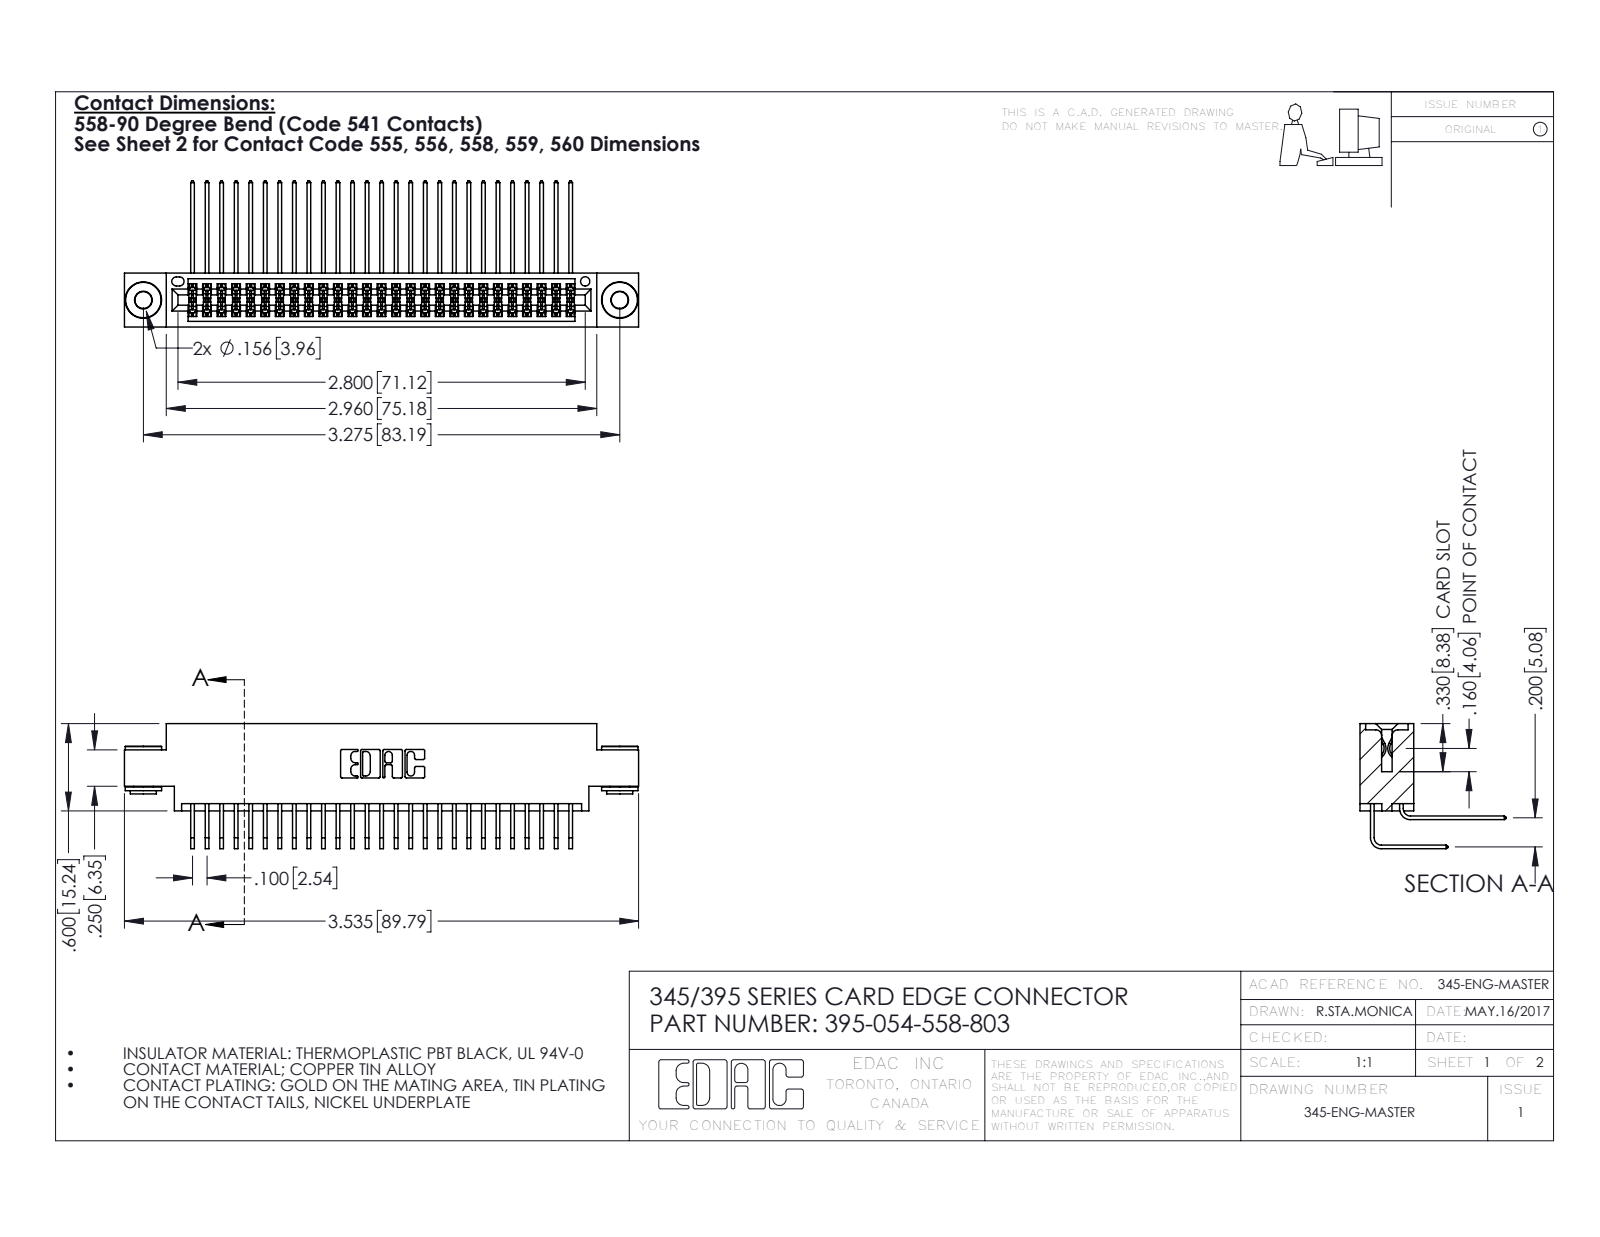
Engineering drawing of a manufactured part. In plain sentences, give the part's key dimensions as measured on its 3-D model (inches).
The part is named "345 Part_0.170 Offset - 0.156 Dia-TH; 345-250-002_345-250-002-102; 345-292-001_558 559 Tail - 1; 395-054-558-803 (+1 more)". Its 3-D file was written by "SolidWorks 2016 (CONFIG_CONTROL_DESIGN)". It is 57 solids with 2976 faces: 1984 planar, 984 cylindrical and 8 other. Overall it measures 3.535 by 1.005 by 0.859 inches. Its volume is 0.537 cubic inches and its surface area 22.52 square inches. Round holes: 2 of diameter 0.116, 2 of diameter 0.156, 1 of diameter 0.064. Round bosses or shafts: 2 of diameter 0.25, 2 of diameter 0.18, 2 of diameter 0.136. Partial cylindrical surfaces (rounded edges, fillets, slot ends): 82 of radius 0.006, 22 of radius 0.01, 6 of radius 0.007, 6 of radius 0.031, 3 of radius 0.026, 2 of radius 0.014, 2 of radius 0.019, 2 of radius 0.022. The main face-to-face distances are 0.072, 0.298, 0.2, 0.37, 0.098, 0.272, 0.025, 0.225, 0.175, 0.025. The hole center spacings are 0.27, 3.04, 3.275.
